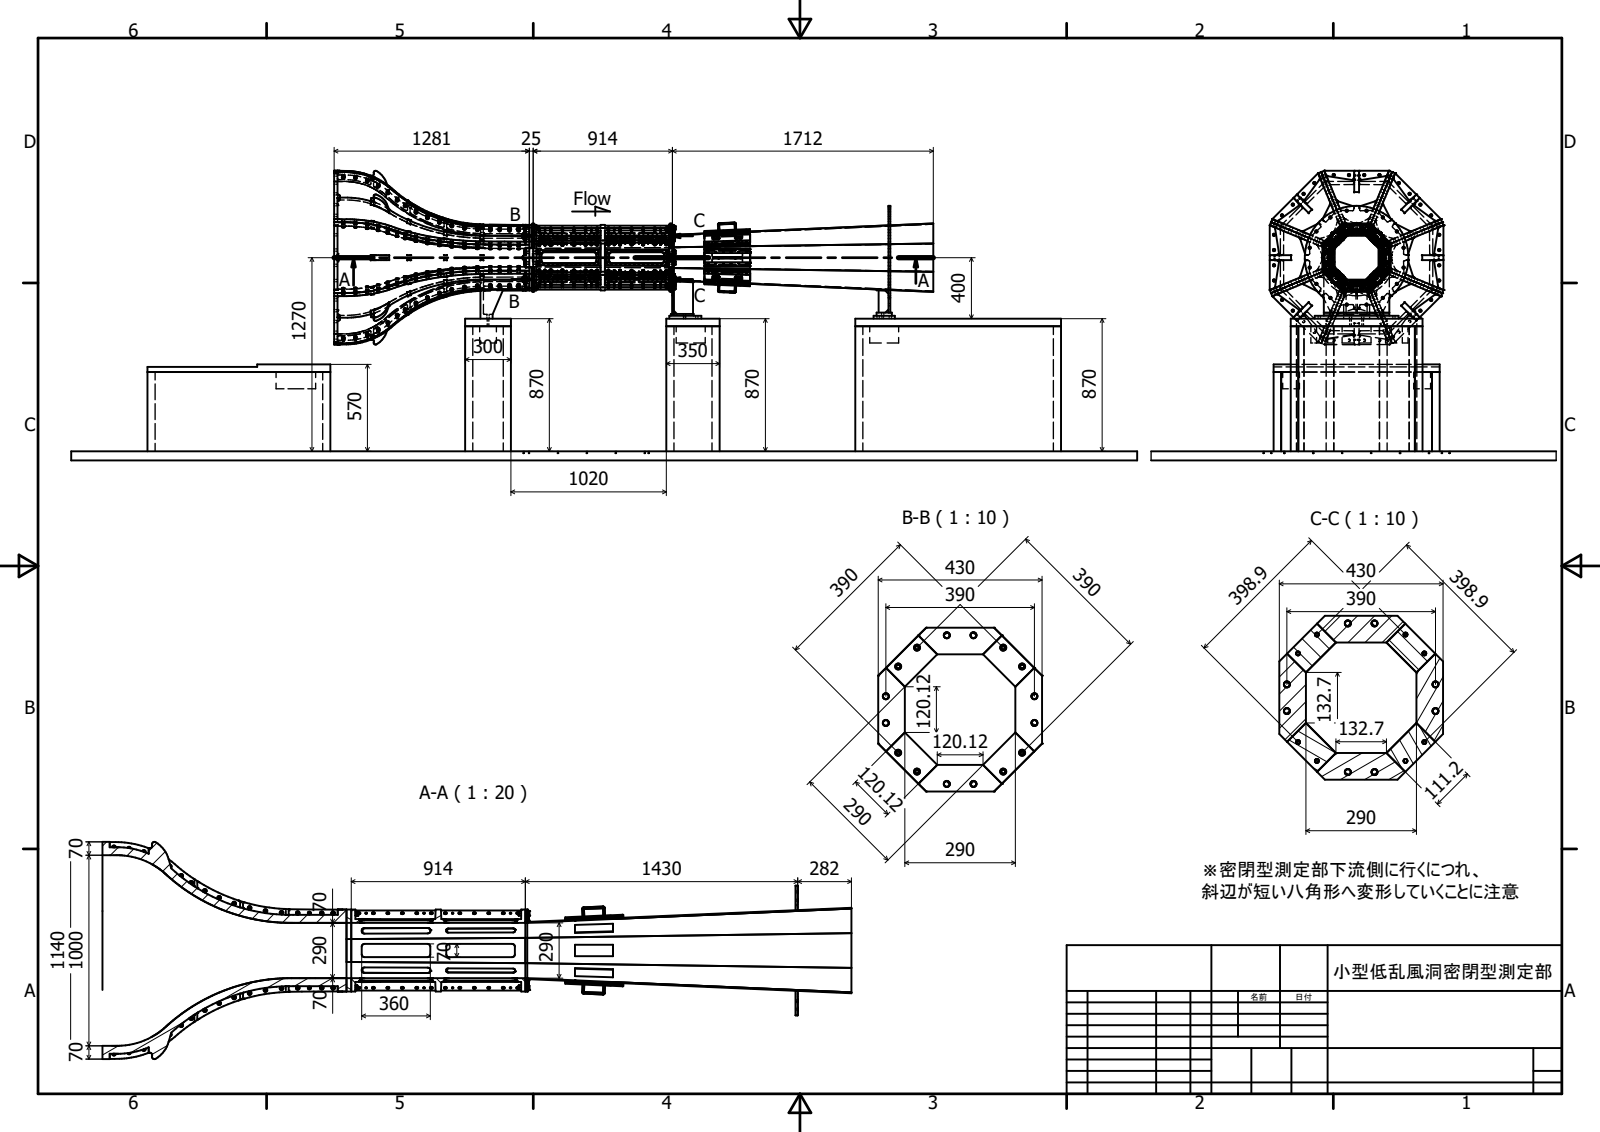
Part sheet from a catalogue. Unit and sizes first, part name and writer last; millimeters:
Units: millimetres
Overall size (bounding box): 6995 × 4490 × 1900
Round holes (diameter × count): ⌀4.2 ×344, ⌀5.5 ×224, ⌀15 ×178, ⌀19 ×150, ⌀10.2 ×112, ⌀5 ×80, ⌀6 ×48, ⌀6.65 ×42, ⌀8 ×32, ⌀16 ×31, ⌀14 ×8, ⌀10.8 ×6
Round bosses / shafts (diameter × count): ⌀9 ×40, ⌀16 ×17, ⌀24 ×16, ⌀10 ×8
Partial cylindrical surfaces — rounded edges, fillets, slot ends (radius × count): R7 ×153, R15 ×128, R10 ×32, R13 ×16, R16 ×12, R150 ×8, R250 ×1, R340 ×1
Main face-to-face distances: 60, 50, 300, 350, 112.5, 927.5, 815, 4.5, 880, 820
Hole centre spacings: 150, 50, 89.31, 30, 100, 60, 85, 424.85
Volume: 2 598 000 000 mm³ · Surface area: 113 700 000 mm²
Bodies: 212 solids, 7333 faces (2277 planar, 2127 cylindrical, 2929 other)
Part name (STEP PRODUCT): 小型低乱風洞（総組）; 測定部台座; 測定部台座A; 測定部台座A_01 (+8 more)
STEP written by: Autodesk Inventor 2023 (AUTOMOTIVE_DESIGN)
